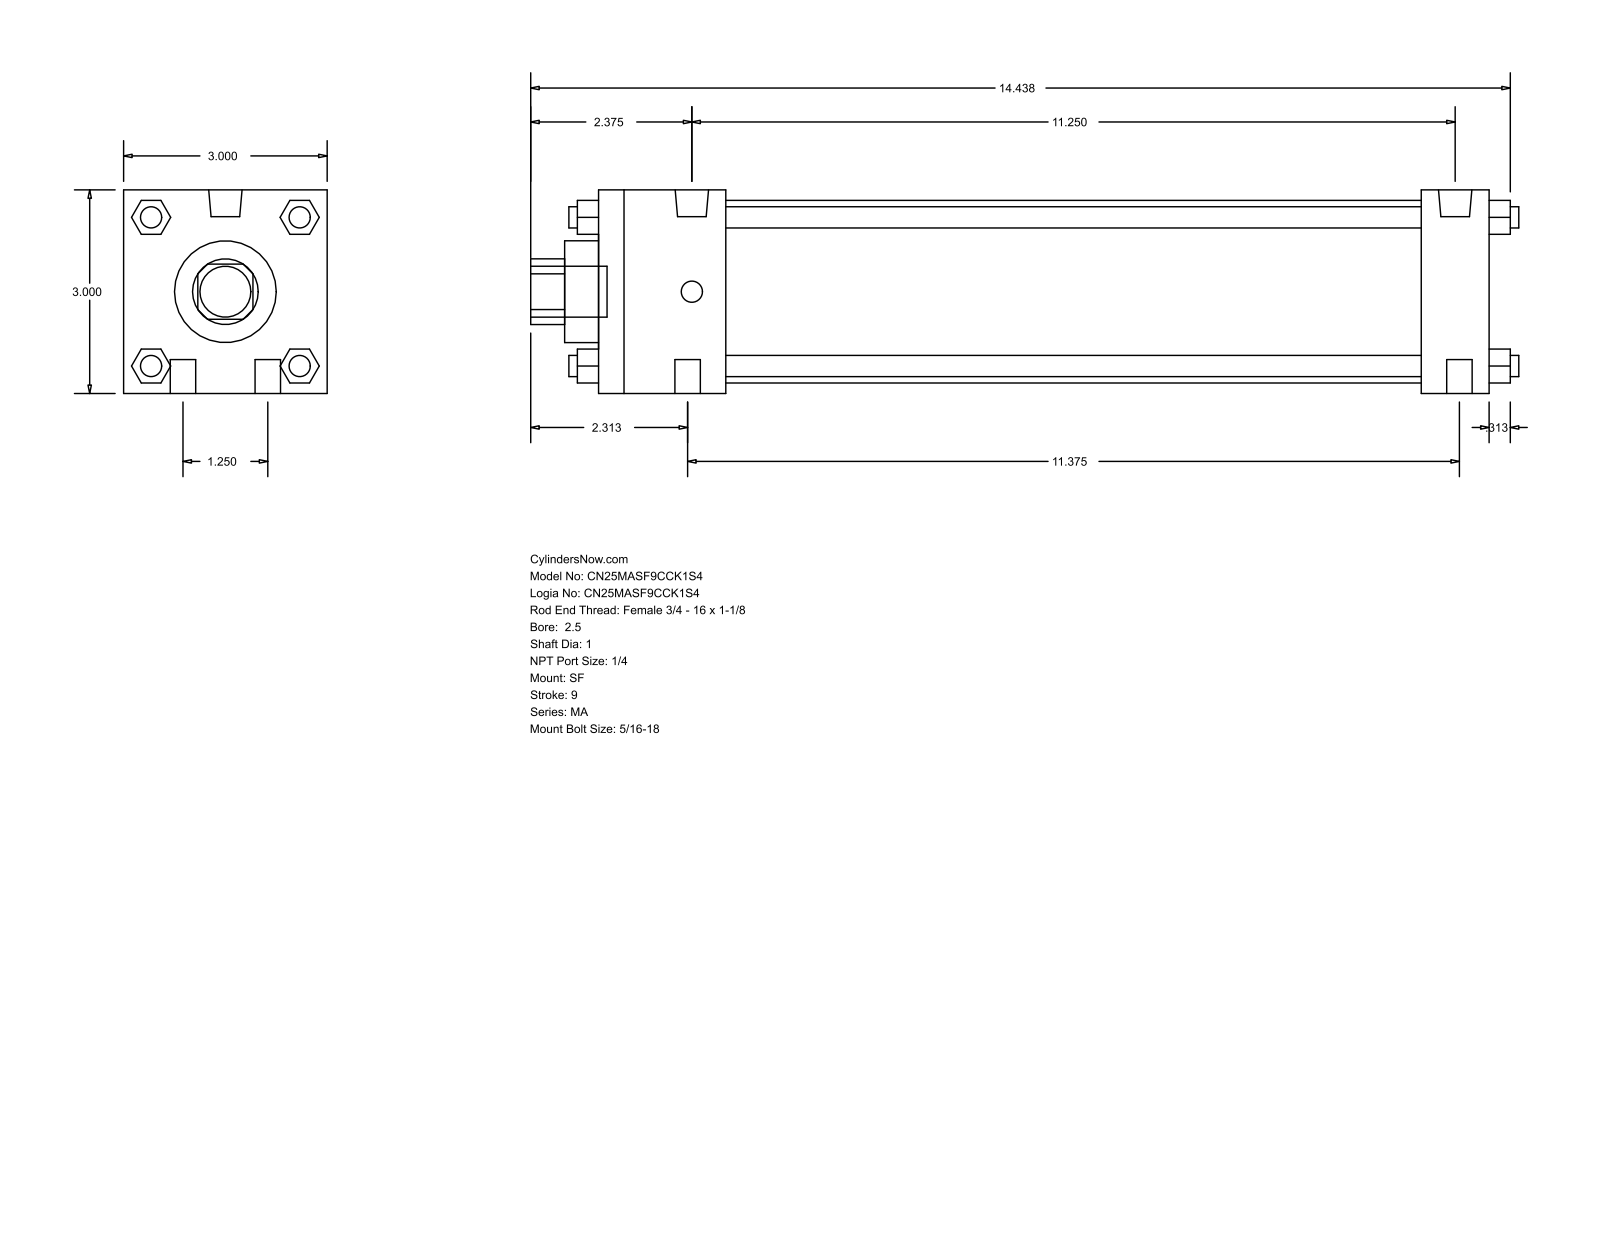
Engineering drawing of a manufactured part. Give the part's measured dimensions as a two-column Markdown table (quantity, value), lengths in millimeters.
| quantity | value |
| --- | --- |
| part name | MA_SF__0250_1 |
| STEP written by | GSSL Pune (CONFIG_CONTROL_DESIGN) |
| units | millimeters |
| bodies | 0 solids, 124 faces (94 planar, 30 cylindrical, 0 other) |
| overall size | 369.89 × 76.2 × 76.2 |
| round holes (diameter × count) | 25.4 × 1, 38.1 × 1, 68.33 × 1 |
| round bosses / shafts (diameter × count) | 7.94 × 6, 9.53 × 4, 12.49 × 2, 19.05 × 1 |
| partial cylindrical surfaces (radius × count) | 12.29 × 1 |
| main face-to-face distances | 76.2, 333.37, 12.7, 307.98, 25.39, 47.63, 260.35, 285.74, 27.81, 48.17 |
